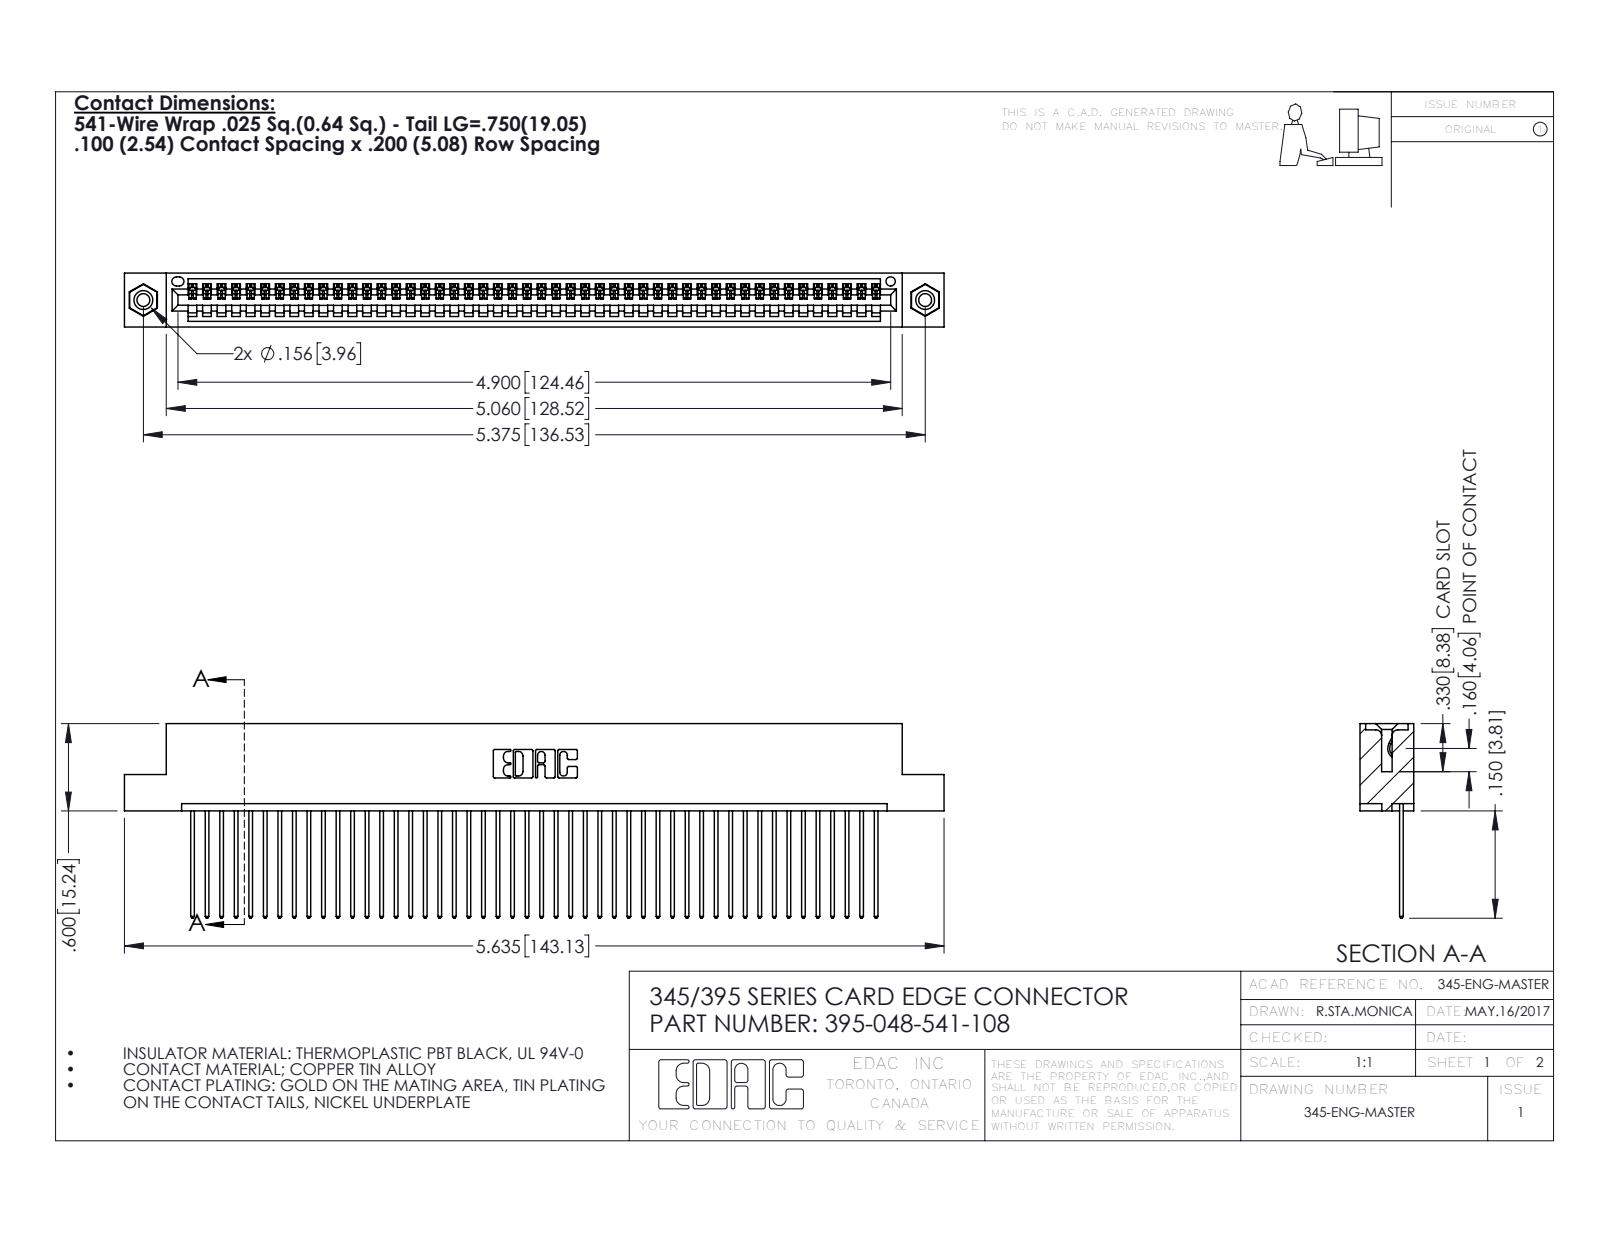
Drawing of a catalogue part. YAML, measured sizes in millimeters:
part_name: "345 Part_Flush Mounting Lugs - 0.156 Dia-TI; 395-048-541-108; 345-250-001_345-250-003-102; 345-292-001_345-293-141"
step_written_by: "SolidWorks 2016 (CONFIG_CONTROL_DESIGN)"
units: millimeters
bodies: {solids: 51, faces: 2970, planar: 2032, cylindrical: 922, other: 16}
overall_size: [143.1, 34, 9.4]
volume: 13800
surface_area: 19370
round_holes:
  - {diameter: 2.3, count: 2}
  - {diameter: 3.2, count: 2}
  - {diameter: 4, count: 2}
  - {diameter: 1.6, count: 1}
round_bosses_or_shafts:
  - {diameter: 3.9, count: 2}
partial_cylinders:
  - {radius: 0.2, count: 96}
  - {radius: 0.3, count: 96}
  - {radius: 0.3, count: 22}
  - {radius: 0.2, count: 6}
  - {radius: 0.8, count: 6}
  - {radius: 0.7, count: 3}
  - {radius: 0.8, count: 2}
  - {radius: 1, count: 2}
face_to_face_distances: [1.8, 7.6, 2.5, 6.9, 0.6, 9.4, 5.1, 5.7, 3.8, 1.8]
hole_center_spacings: [6.9, 130.5, 136.5]
